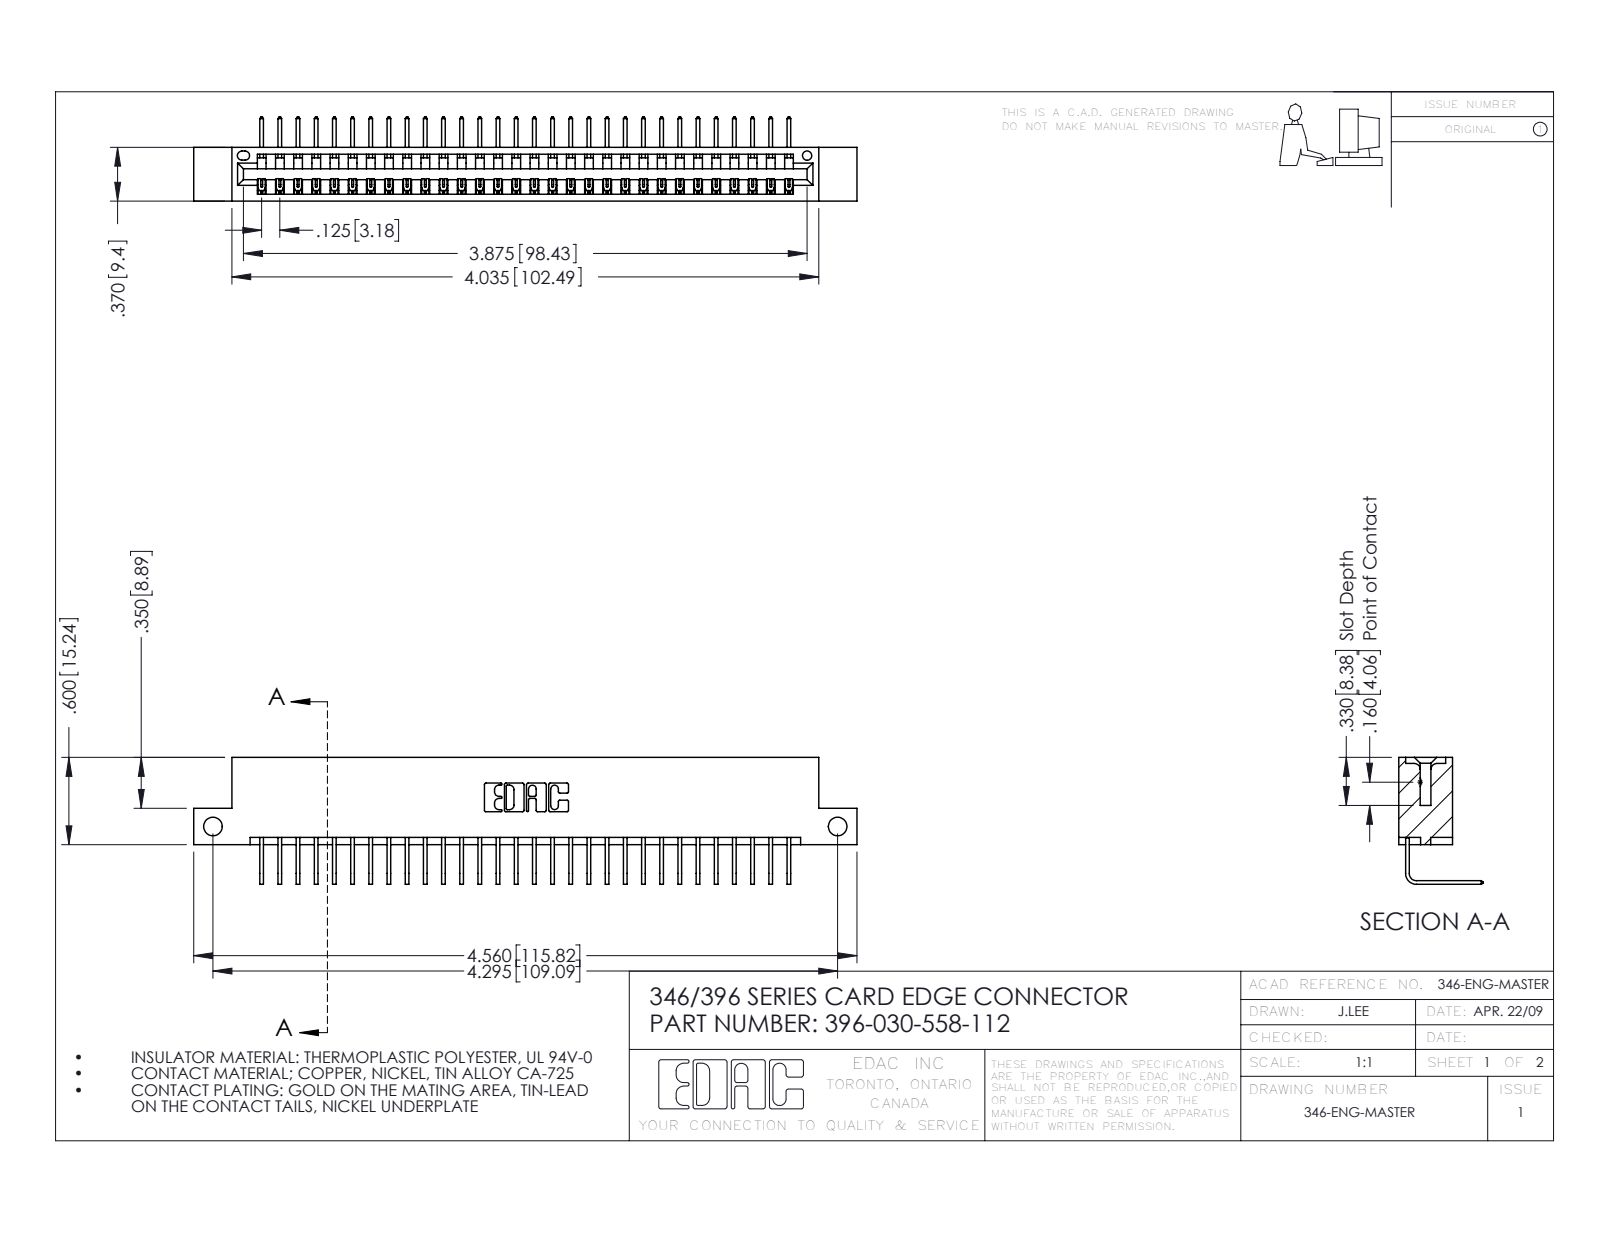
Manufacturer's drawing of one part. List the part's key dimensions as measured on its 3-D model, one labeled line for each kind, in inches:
Part name (STEP PRODUCT): 345-292-001_558 Tail - 2; 396-030-558-112; 346 Part_Flush Mounting Lugs - Side Mount
STEP written by: SolidWorks 2016 (CONFIG_CONTROL_DESIGN)
Units: inches
Bodies: 31 solids, 1922 faces (1336 planar, 586 cylindrical, 0 other)
Overall size (bounding box): 4.56 × 0.873 × 0.58
Volume: 0.672 in³ · Surface area: 21.84 in²
Round holes (diameter × count): ⌀0.128 ×2, ⌀0.064 ×1
Partial cylindrical surfaces — rounded edges, fillets, slot ends (radius × count): R0.006 ×60, R0.01 ×22, R0.007 ×6, R0.031 ×6, R0.026 ×3, R0.031 ×2, R0.04 ×2, R0.014 ×1
Main face-to-face distances: 0.322, 0.048, 0.37, 0.25, 0.298, 0.025, 0.072, 0.148, 0.222, 0.1
Hole centre spacings: 4.295
